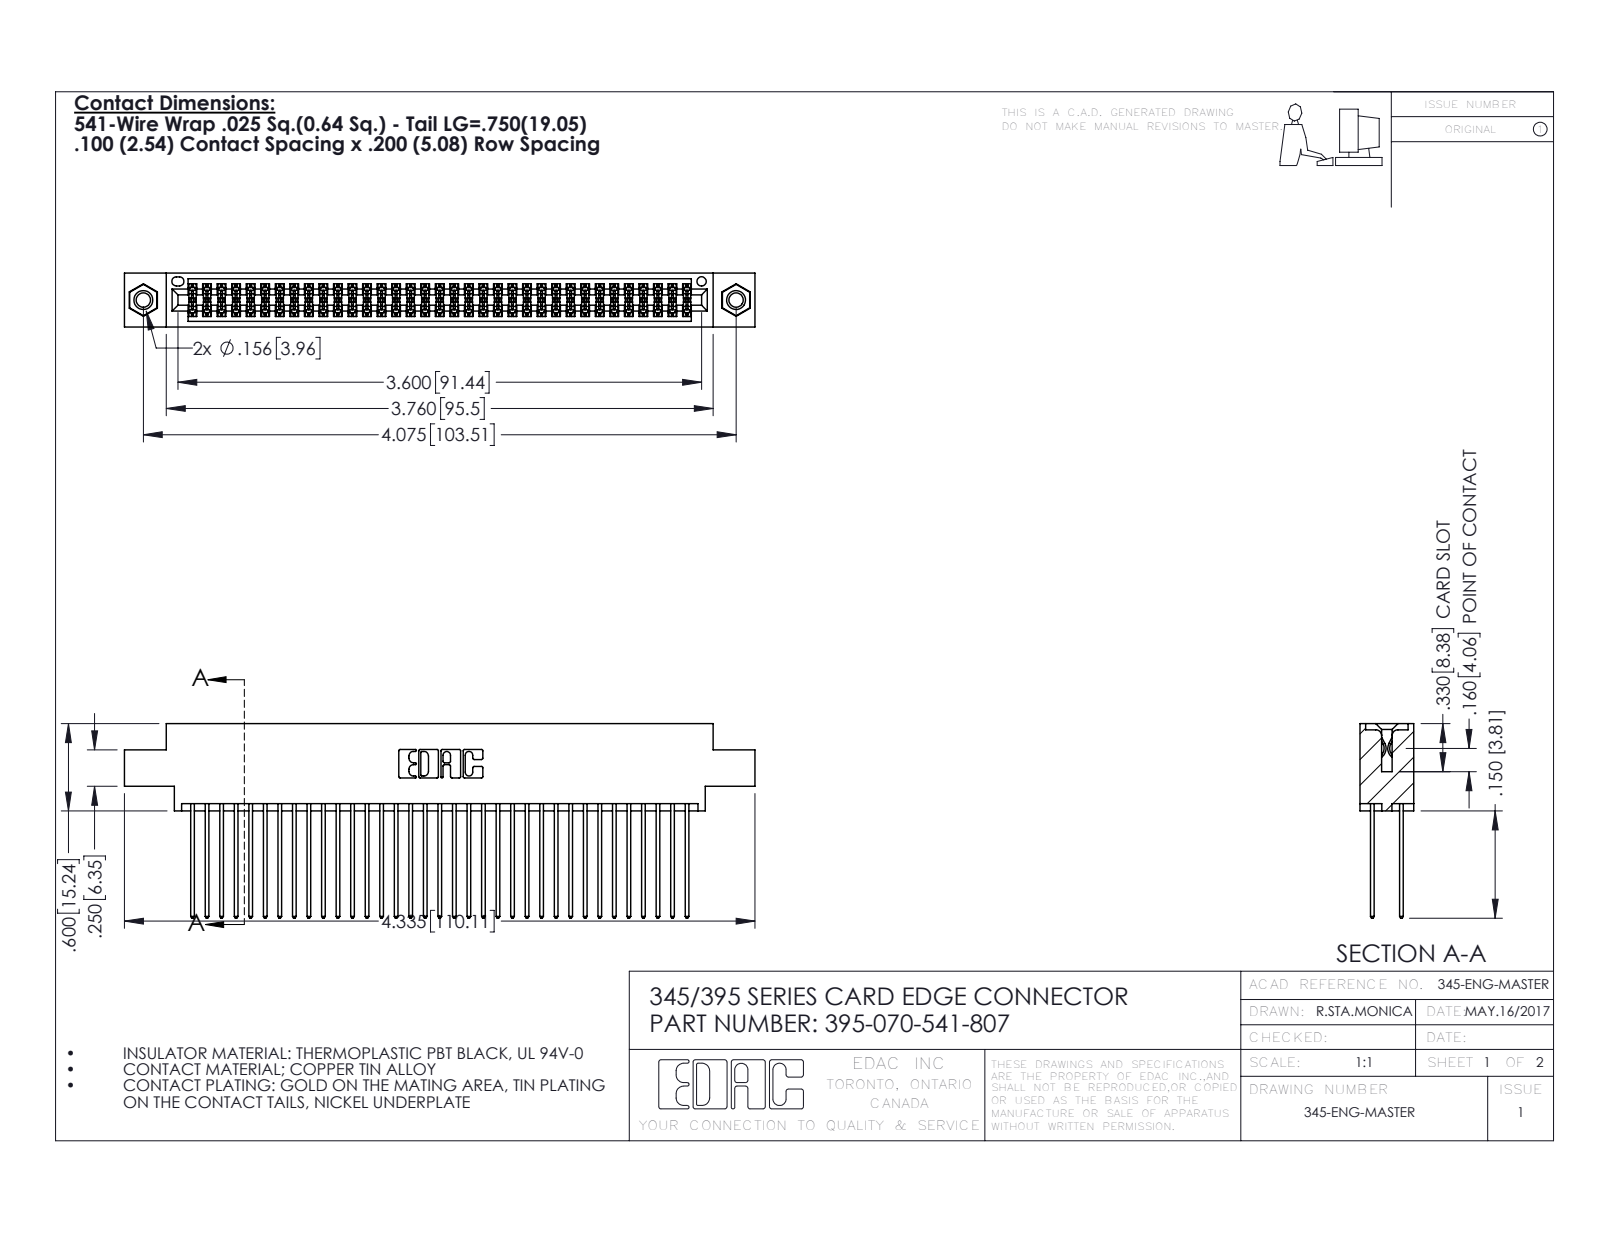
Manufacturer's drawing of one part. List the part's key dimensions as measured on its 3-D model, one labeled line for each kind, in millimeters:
Part name (STEP PRODUCT): 395-070-541-807; 345-292-001_345-293-141; 345 Part_0.170 Offset - 0.156 Dia-TI; 345-250-001_345-250-005-103
STEP written by: SolidWorks 2016 (CONFIG_CONTROL_DESIGN)
Units: millimetres
Bodies: 73 solids, 3690 faces (2426 planar, 1248 cylindrical, 16 other)
Overall size (bounding box): 110.1 × 34 × 9.4
Volume: 10 900 mm³ · Surface area: 18 050 mm²
Round holes (diameter × count): ⌀2.5 ×2, ⌀3.2 ×2, ⌀4 ×2, ⌀1.6 ×1
Round bosses / shafts (diameter × count): ⌀3.9 ×2
Partial cylindrical surfaces — rounded edges, fillets, slot ends (radius × count): R0.2 ×105, R0.3 ×70, R0.3 ×22, R0.2 ×6, R0.8 ×6, R0.7 ×3, R0.4 ×2, R0.5 ×2
Main face-to-face distances: 1.8, 7.6, 5.1, 2.5, 6.9, 0.6, 9.4, 5.7, 4.4, 3.8
Hole centre spacings: 6.9, 97.5, 103.5
